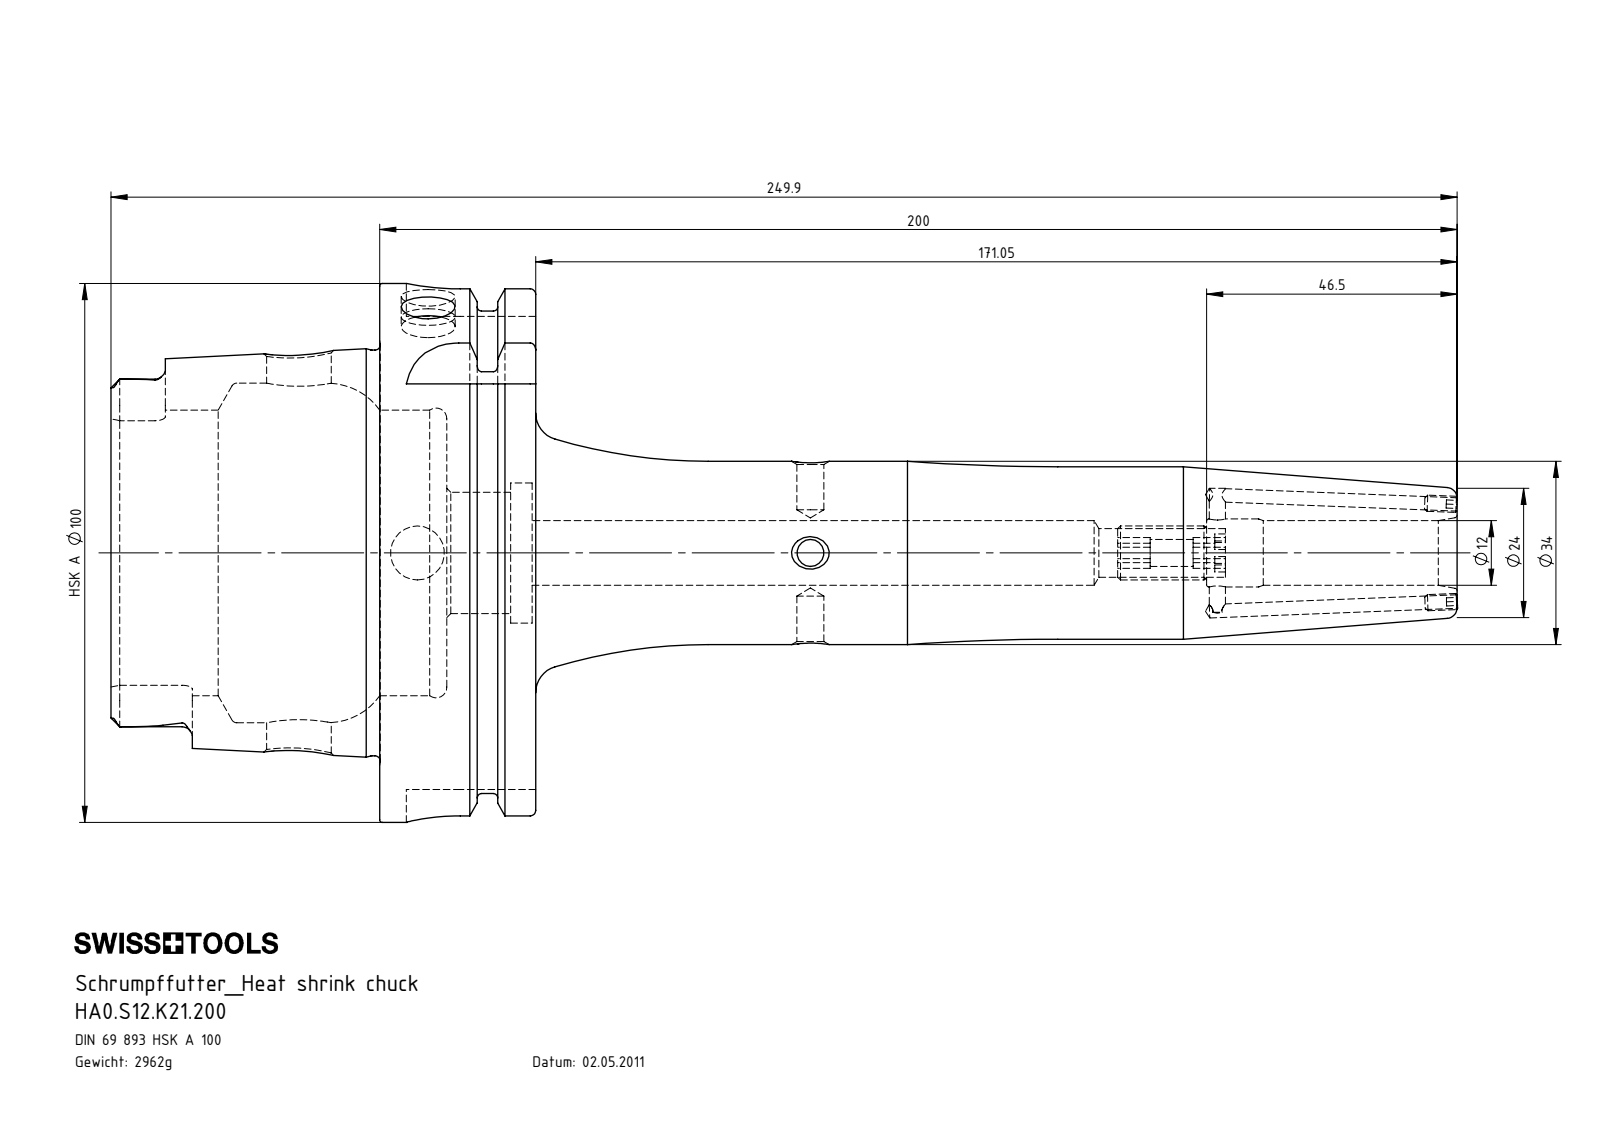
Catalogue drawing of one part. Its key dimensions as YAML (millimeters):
part_name: "HA0-S12.K21.200_C_Fertigbearbeitung; ERU-CJ2.001.006; ERU-AN4.K01.020_A; HA0.S12.K21.200"
step_written_by: "SolidWorks 2017 (CONFIG_CONTROL_DESIGN)"
units: millimeters
bodies: {solids: 4, faces: 299, planar: 95, cylindrical: 86, other: 118}
overall_size: [249.98, 100, 100]
volume: 377284
surface_area: 74720
round_holes:
  - {diameter: 5, count: 3}
  - {diameter: 10, count: 3}
  - {diameter: 2.5, count: 2}
  - {diameter: 12, count: 2}
  - {diameter: 3, count: 1}
  - {diameter: 9, count: 1}
  - {diameter: 12.6, count: 1}
  - {diameter: 22.5, count: 1}
  - {diameter: 26, count: 1}
  - {diameter: 53, count: 1}
  - {diameter: 63, count: 1}
round_bosses_or_shafts:
  - {diameter: 3, count: 2}
  - {diameter: 100, count: 1}
  - {diameter: 91.95, count: 1}
  - {diameter: 75.26, count: 1}
  - {diameter: 34, count: 1}
  - {diameter: 32, count: 1}
  - {diameter: 10, count: 1}
partial_cylinders:
  - {radius: 1.9, count: 6}
  - {radius: 4.88, count: 4}
  - {radius: 10, count: 4}
face_to_face_distances: [28.95, 16.5, 12.45, 49.9, 62.35, 78.85, 87.8, 78.2, 28.3, 15.85]
hole_center_spacings: [72.95, 75.55, 94.95, 170.5]
